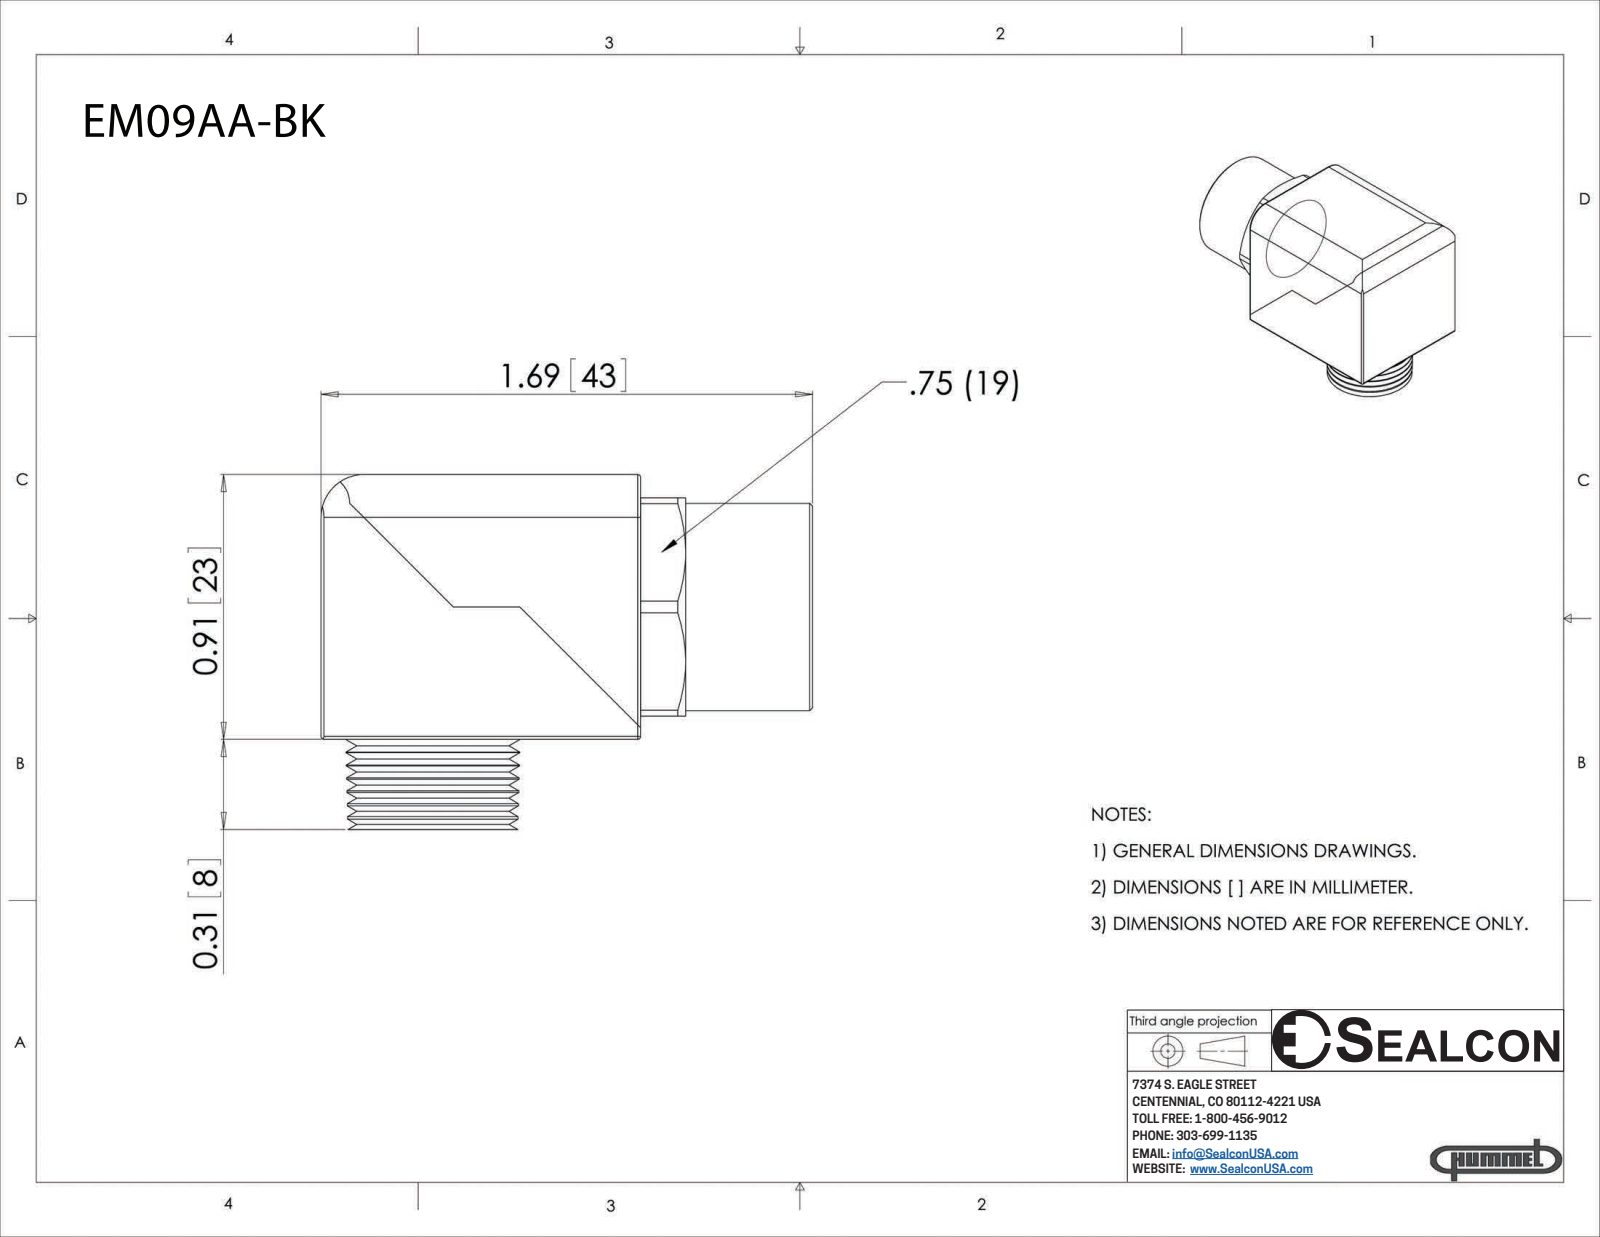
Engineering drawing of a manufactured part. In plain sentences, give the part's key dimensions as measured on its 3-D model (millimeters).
The part is named "EM09AA-BK". Its 3-D file was written by "SolidWorks 2007 (AUTOMOTIVE_DESIGN)". It is 2 solids with 126 faces: 31 planar, 34 cylindrical and 61 other. Overall it measures 42.9 by 31 by 23.1 millimeters. Its volume is 15 600 cubic millimeters and its surface area 8 181 square millimeters. Round holes: 2 of diameter 8.4, 1 of diameter 15.2. Round bosses or shafts: 1 of diameter 18.1. Partial cylindrical surfaces (rounded edges, fillets, slot ends): 7 of radius 0.3, 3 of radius 3.7, 1 of radius 2.5, 1 of radius 10.7. The main face-to-face distances are 23.1, 4.1, 27.9, 11.6, 3.9, 31.9, 7.9, 19.4, 31, 19.1.
